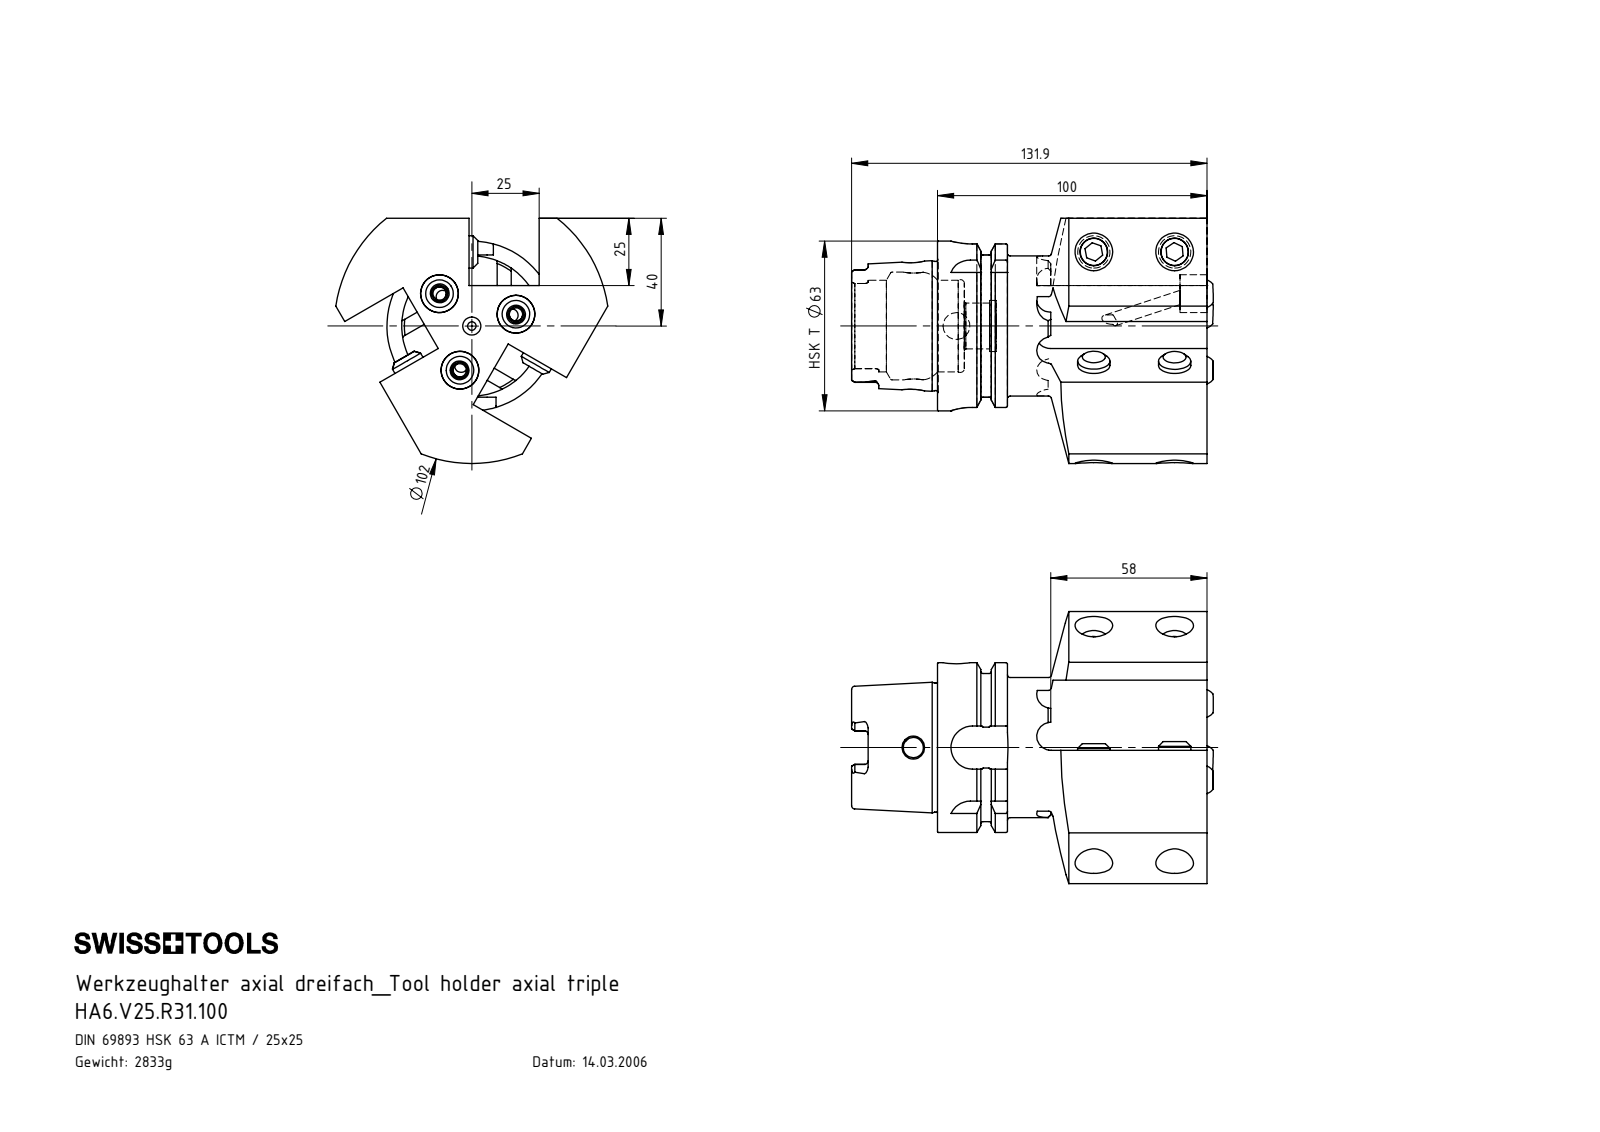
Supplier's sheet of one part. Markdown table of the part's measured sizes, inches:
| quantity | value |
| --- | --- |
| part name | KU1-U14.001.012_1; KU1-U14.001.012; ISO 4026 - M12 x 25; HA6.V25.R31.100 (+2 more) |
| STEP written by | SolidWorks 2017 (AUTOMOTIVE_DESIGN) |
| units | inches |
| bodies | 13 solids, 292 faces (127 planar, 74 cylindrical, 91 other) |
| overall size | 5.304 × 3.973 × 3.583 |
| volume | 22.13 in³ |
| surface area | 122.8 in² |
| round holes (diameter × count) | 0.551 × 9, 0.197 × 6, 0.404 × 6, 0.394 × 4, 0.124 × 1, 0.295 × 1, 0.331 × 1, 0.669 × 1, 0.748 × 1, 1.339 × 1, 1.575 × 1 |
| round bosses / shafts (diameter × count) | 0.472 × 6, 2.48 × 1, 2.163 × 1, 2.047 × 1, 1.887 × 1 |
| partial cylindrical surfaces (radius × count) | 0.055 × 6, 0.205 × 6, 0.113 × 4, 0.315 × 4, 2.008 × 1 |
| main face-to-face distances | 0.984, 1.024, 3.937, 0.63, 0.394, 3.543, 1.022, 2.522, 2.915, 0.392 |
| hole center spacings | 0.668, 1.157, 1.181, 2.281, 3.368 |
